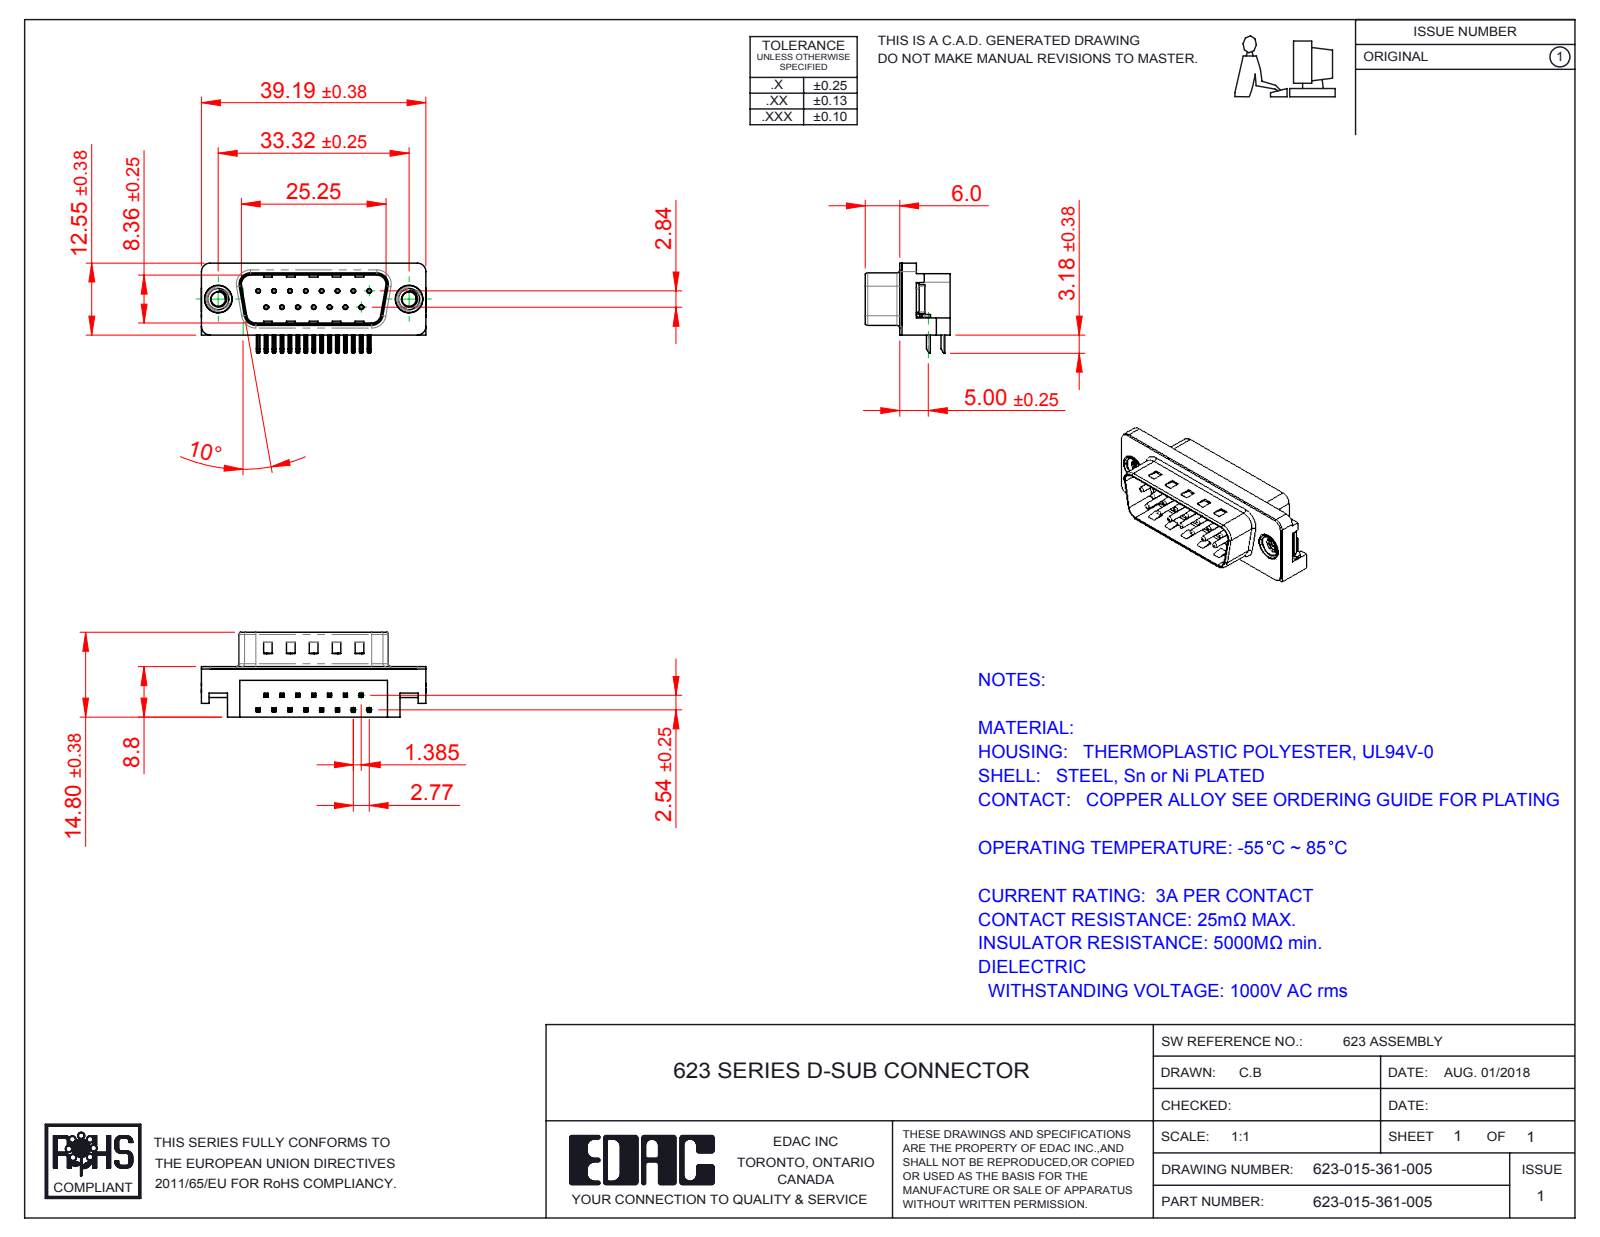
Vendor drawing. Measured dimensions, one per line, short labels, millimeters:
name: 623 Housing_15 Socket; 623 Shell_15 Socket; 623 Contact Bottom; 623-015-361-005 (+3 more)
written by: SolidWorks 2016 (CONFIG_CONTROL_DESIGN)
unit: mm
bodies: 21 solids, 1467 faces (893 planar, 439 cylindrical, 135 other)
size: 39.22 × 15.73 × 14.8
volume: 3 313 mm³; area: 4 888 mm²
holes: 15× ⌀0.35, 15× ⌀0.8, 2× ⌀2.5, 2× ⌀4, 2× ⌀4.8, 2× ⌀5
bosses: 15× ⌀0.75, 2× ⌀4.9, 2× ⌀4.75, 2× ⌀3.9
rounds: 68× R0.25, 30× R0.12, 16× R1, 9× R0.5, 6× R1.5, 4× R0.9, 4× R1.6, 4× R2
face distances: 0.4, 8.4, 2.1, 1.7, 10.46, 8.8, 10.86, 8.76, 5.9, 2.9
hole spacings: 3.16, 2.77, 5.54, 8.31, 11.08, 5.03, 5.04, 7.48
